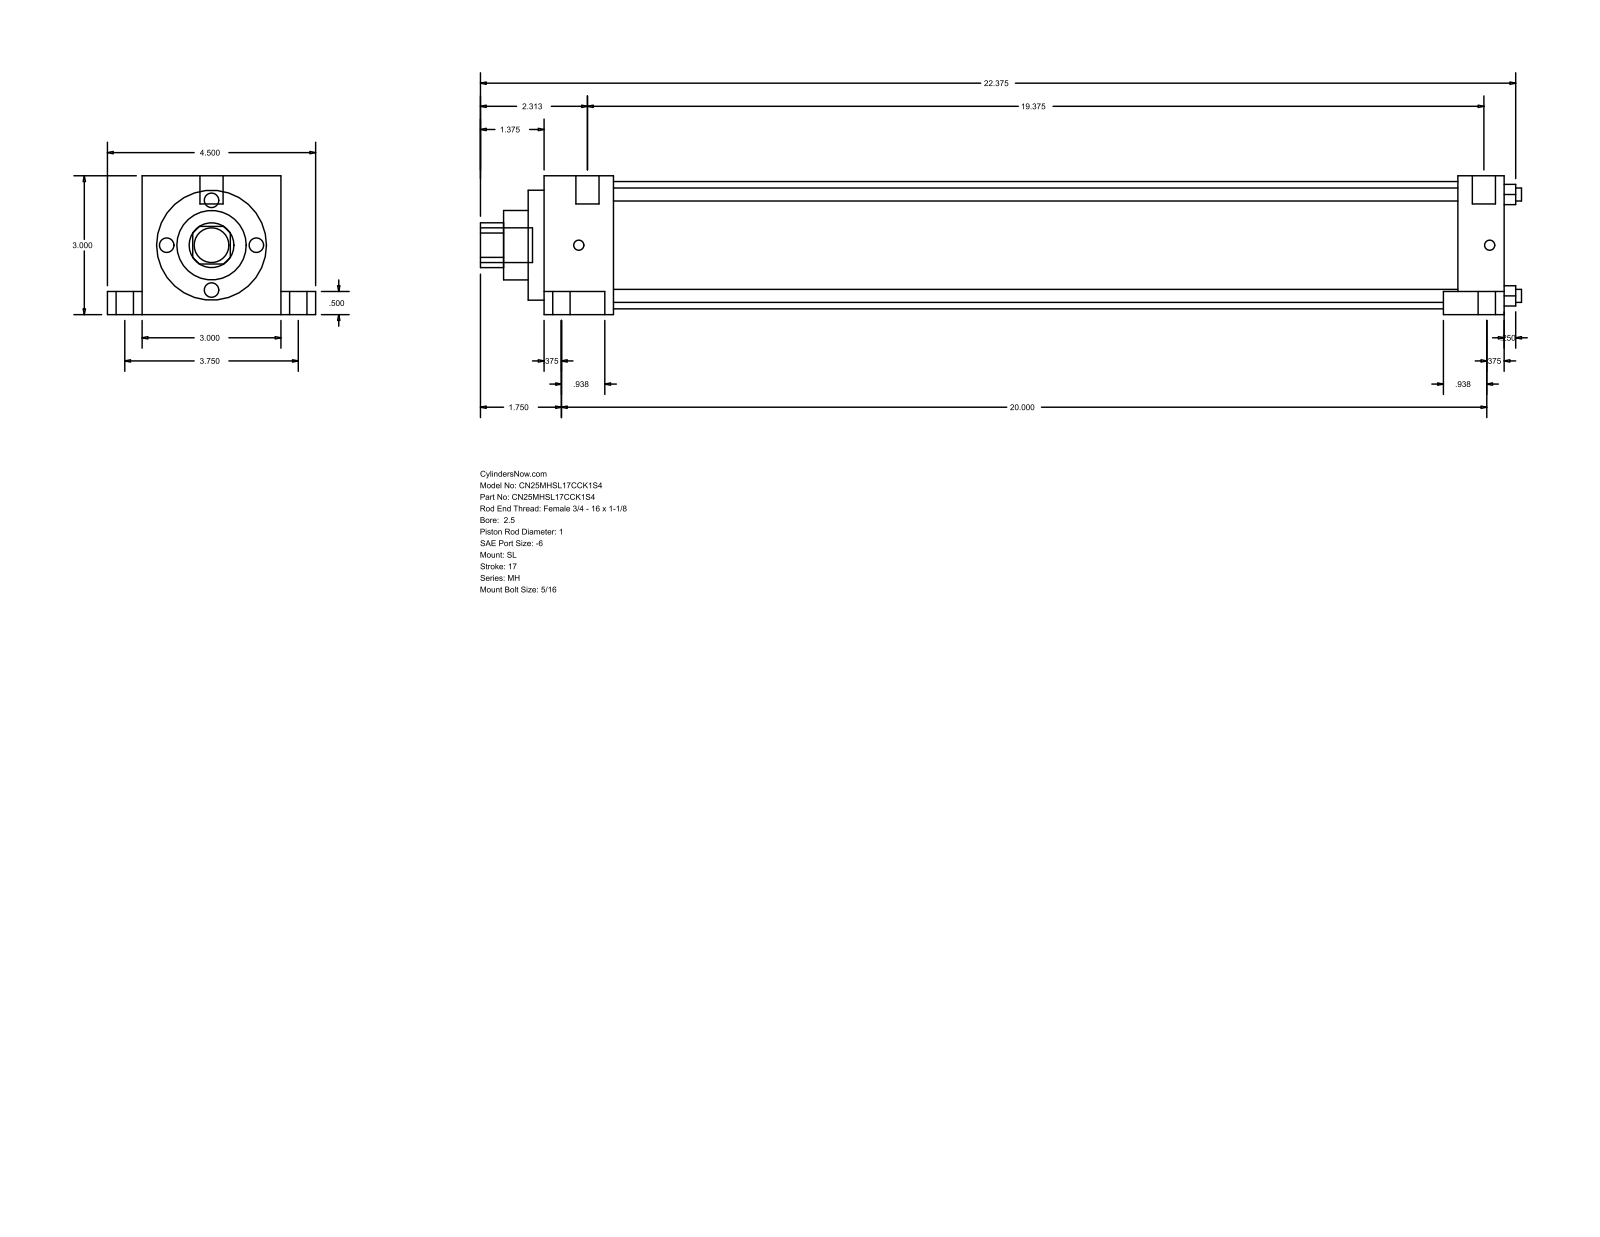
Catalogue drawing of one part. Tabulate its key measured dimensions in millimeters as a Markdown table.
| quantity | value |
| --- | --- |
| part name | MH_SL__0250_1 |
| STEP written by | GSSL Pune (CONFIG_CONTROL_DESIGN) |
| units | millimeters |
| bodies | 0 solids, 86 faces (61 planar, 25 cylindrical, 0 other) |
| overall size | 571.5 × 114.3 × 76.2 |
| round holes (diameter × count) | 7.14 × 4, 25.4 × 1, 38.1 × 1, 60.33 × 1, 69.85 × 1 |
| round bosses / shafts (diameter × count) | 15.88 × 2, 9.53 × 2, 5.56 × 2, 19.05 × 1, 12.7 × 1 |
| partial cylindrical surfaces (radius × count) | 12.29 × 1 |
| main face-to-face distances | 76.2, 25.4, 510.39, 535.79, 12.7, 63.5, 19.05, 95.25, 13.49, 523.88 |
| hole center spacings | 39.33, 55.62, 78.66 |
